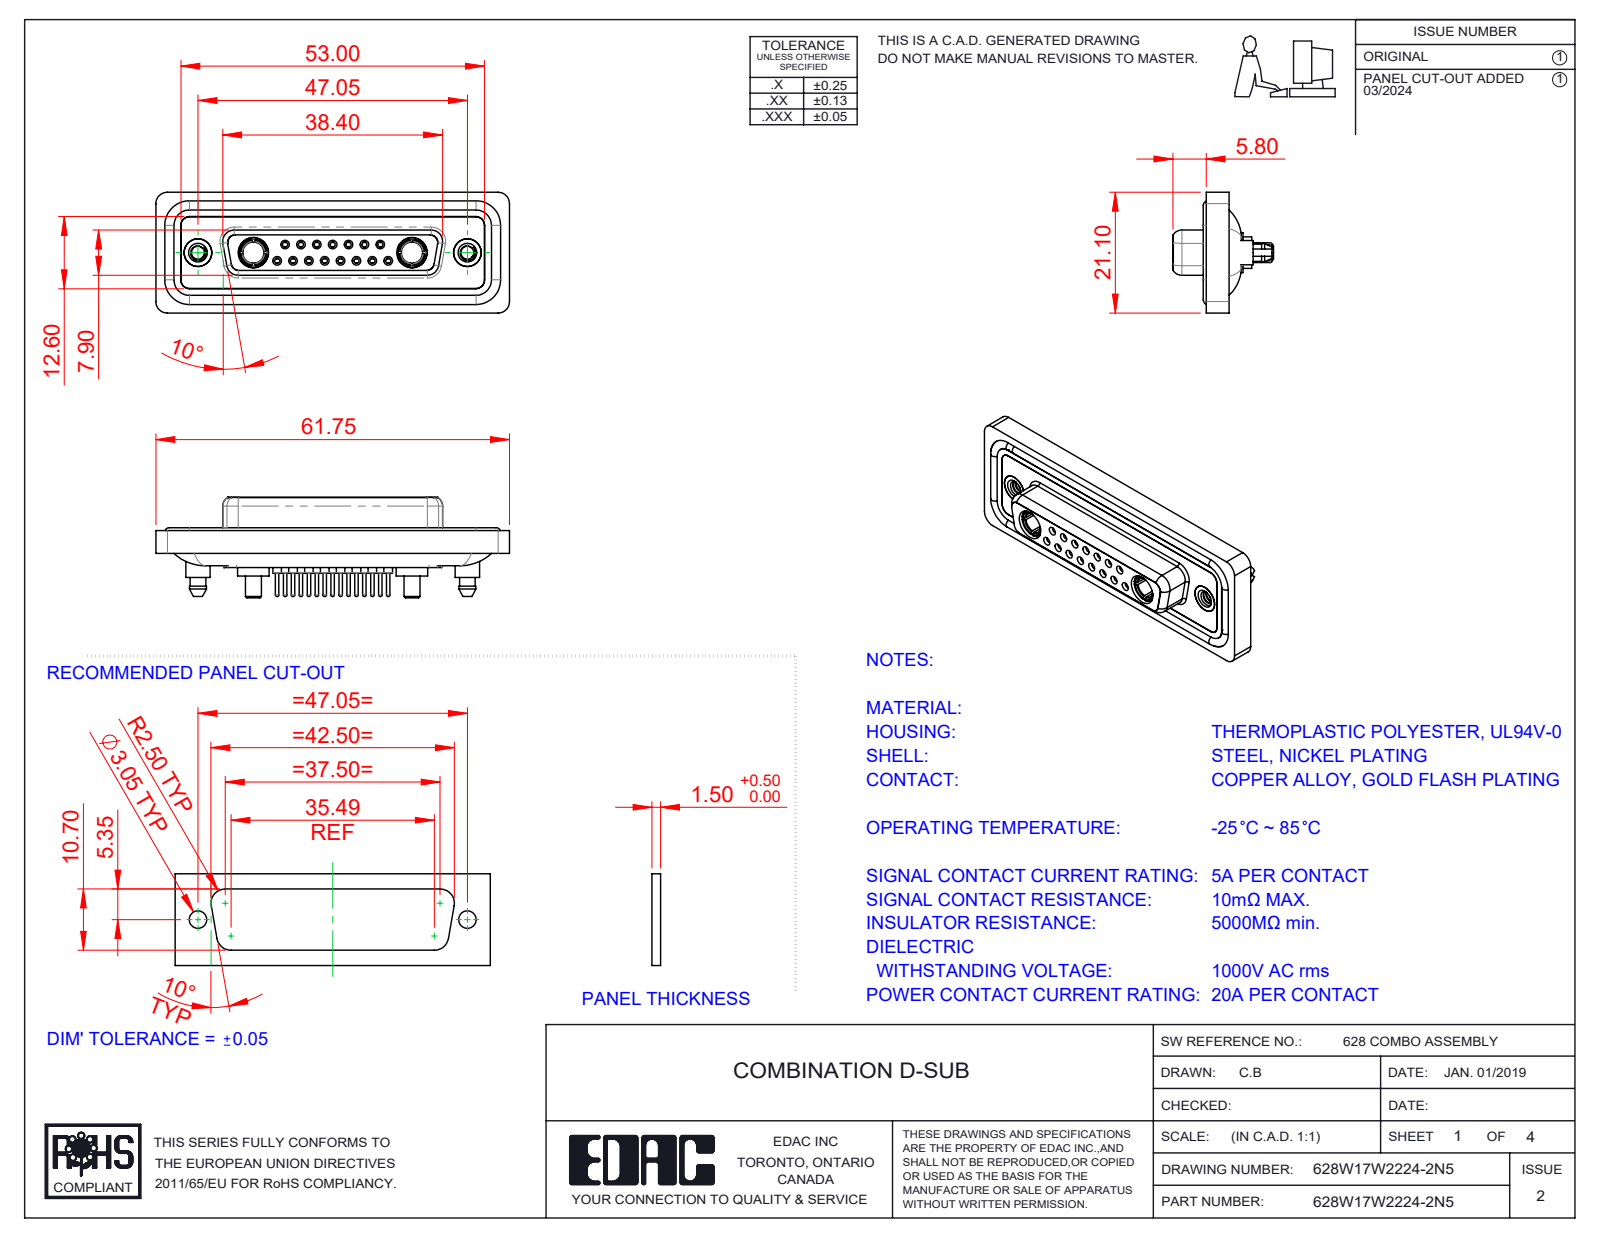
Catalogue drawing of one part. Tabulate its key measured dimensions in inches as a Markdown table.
| quantity | value |
| --- | --- |
| part name | 628Combo Housing_17W2; 628W17W2224-2N5; 628Combo Shell Rear_25 Contacts; 628Combo Contact Row 2_24 (+5 more) |
| STEP written by | SolidWorks 2023 (CONFIG_CONTROL_DESIGN) |
| units | inches |
| bodies | 26 solids, 1409 faces (404 planar, 551 cylindrical, 454 other) |
| overall size | 2.431 × 0.831 × 0.691 |
| volume | 0.516 in³ |
| surface area | 21.99 in² |
| round holes (diameter × count) | 0.035 × 15, 0.043 × 15, 0.059 × 15, 0.079 × 15, 0.063 × 8, 0.067 × 7, 0.191 × 4, 0.089 × 2, 0.146 × 2, 0.157 × 2, 0.159 × 2, 0.197 × 2 |
| round bosses / shafts (diameter × count) | 0.087 × 15, 0.024 × 15, 0.063 × 11, 0.217 × 2, 0.213 × 2, 0.205 × 2, 0.195 × 2, 0.195 × 2 |
| partial cylindrical surfaces (radius × count) | 0.059 × 24, 0.079 × 18, 0.063 × 10, 0.053 × 8, 0.01 × 4, 0.02 × 4, 0.024 × 4, 0.026 × 4 |
| main face-to-face distances | 0.016, 0.071, 0.293, 0.222, 0.26, 0.02, 0.278, 0.063, 0.114, 0.043 |
| hole center spacings | 0.124, 0.109, 0.327, 0.218, 0.198, 0.198, 0.295, 0.436 |
